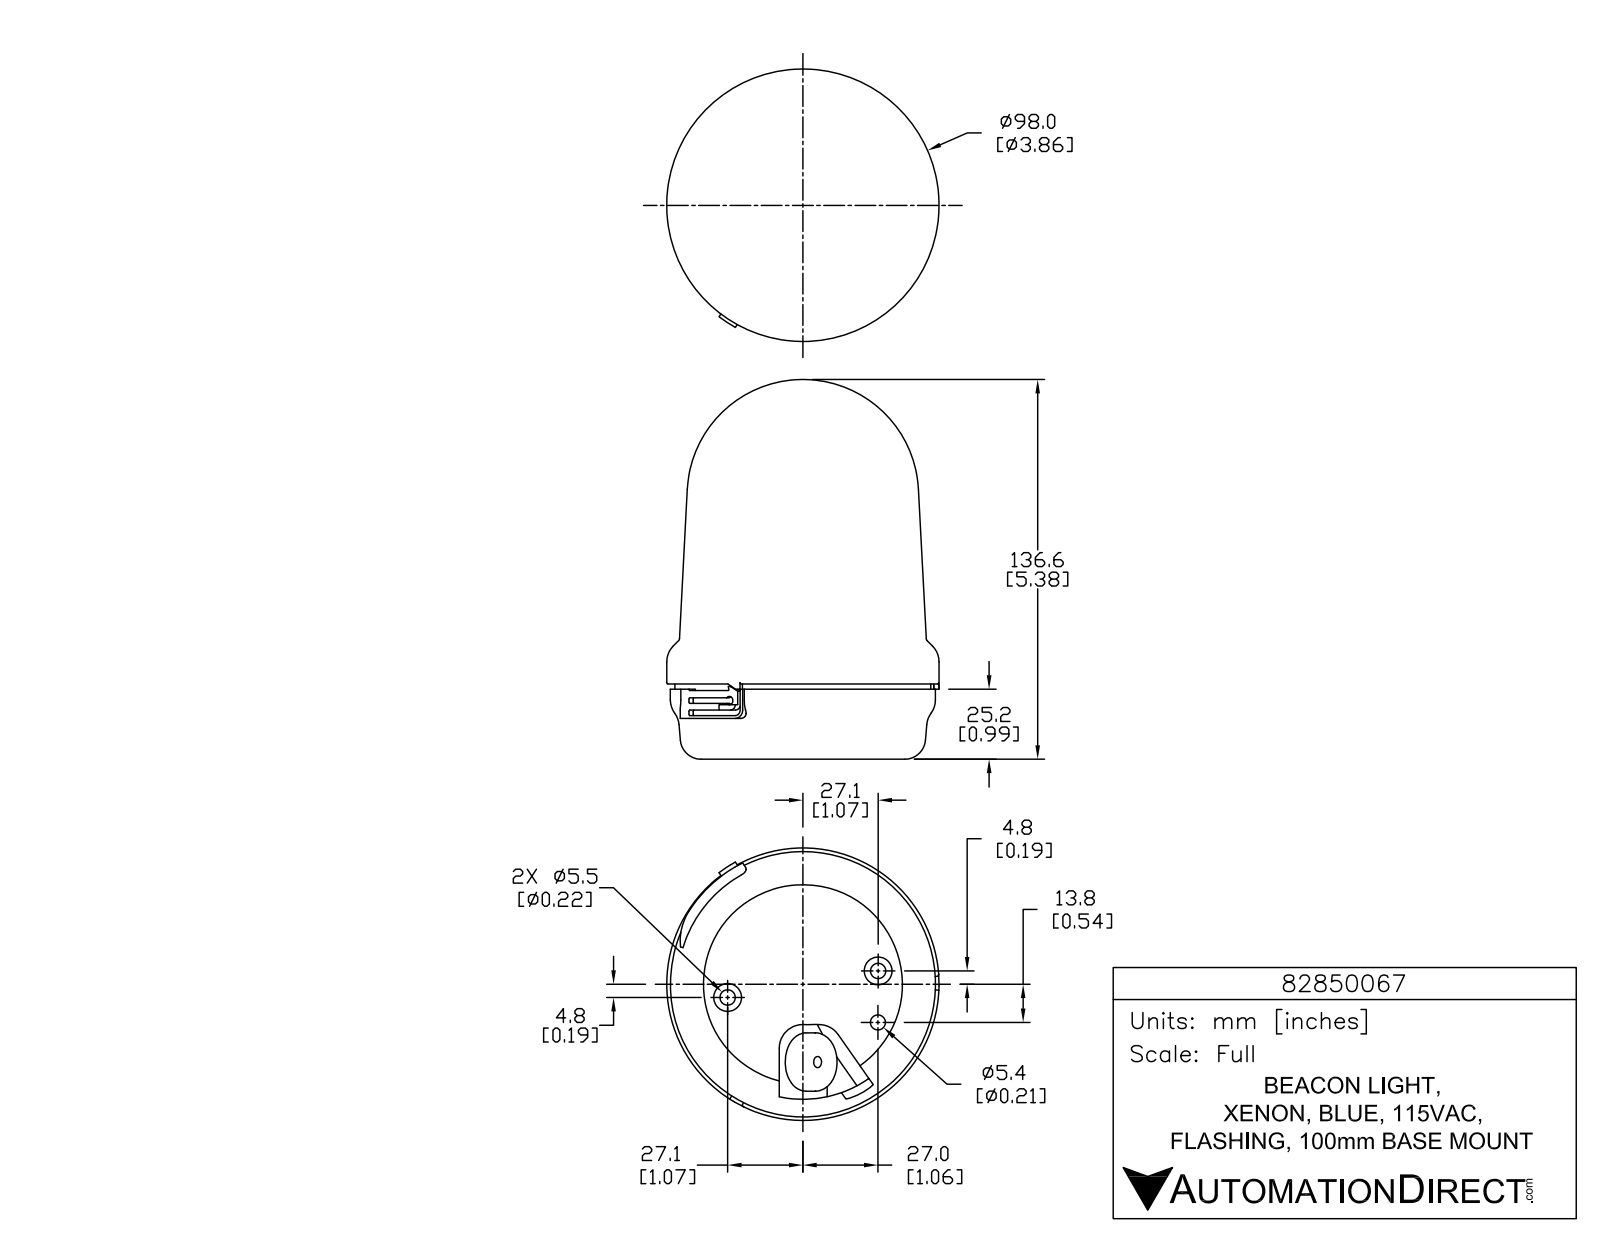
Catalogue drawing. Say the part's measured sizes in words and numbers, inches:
The part is named "82850067". Its 3-D file was written by "SolidWorks 2015 (AUTOMOTIVE_DESIGN)". It is 1 solid with 872 faces: 566 planar, 204 cylindrical and 102 other. Overall it measures 5.378 by 3.858 by 3.858 inches. Its volume is 44.69 cubic inches and its surface area 73.66 square inches. Round holes: 3 of diameter 0.059, 2 of diameter 0.217, 1 of diameter 0.157, 1 of diameter 0.213, 1 of diameter 2.819. Round bosses or shafts: 3 of diameter 0.339, 3 of diameter 0.084, 2 of diameter 0.394, 1 of diameter 3.858, 1 of diameter 3.756, 1 of diameter 3.626, 1 of diameter 0.827. Partial cylindrical surfaces (rounded edges, fillets, slot ends): 9 of radius 0.005, 6 of radius 0.005, 6 of radius 0.012, 6 of radius 0.012, 6 of radius 0.012, 6 of radius 0.196, 5 of radius 0.02, 4 of radius 0.039. The main face-to-face distances are 1.045, 0.972, 0.073, 0.02, 0.992, 1.065, 0.236, 0.579, 0.559, 0.413. The hole center spacings are 1.083, 0.73, 1.193, 2.158, 2.165.
